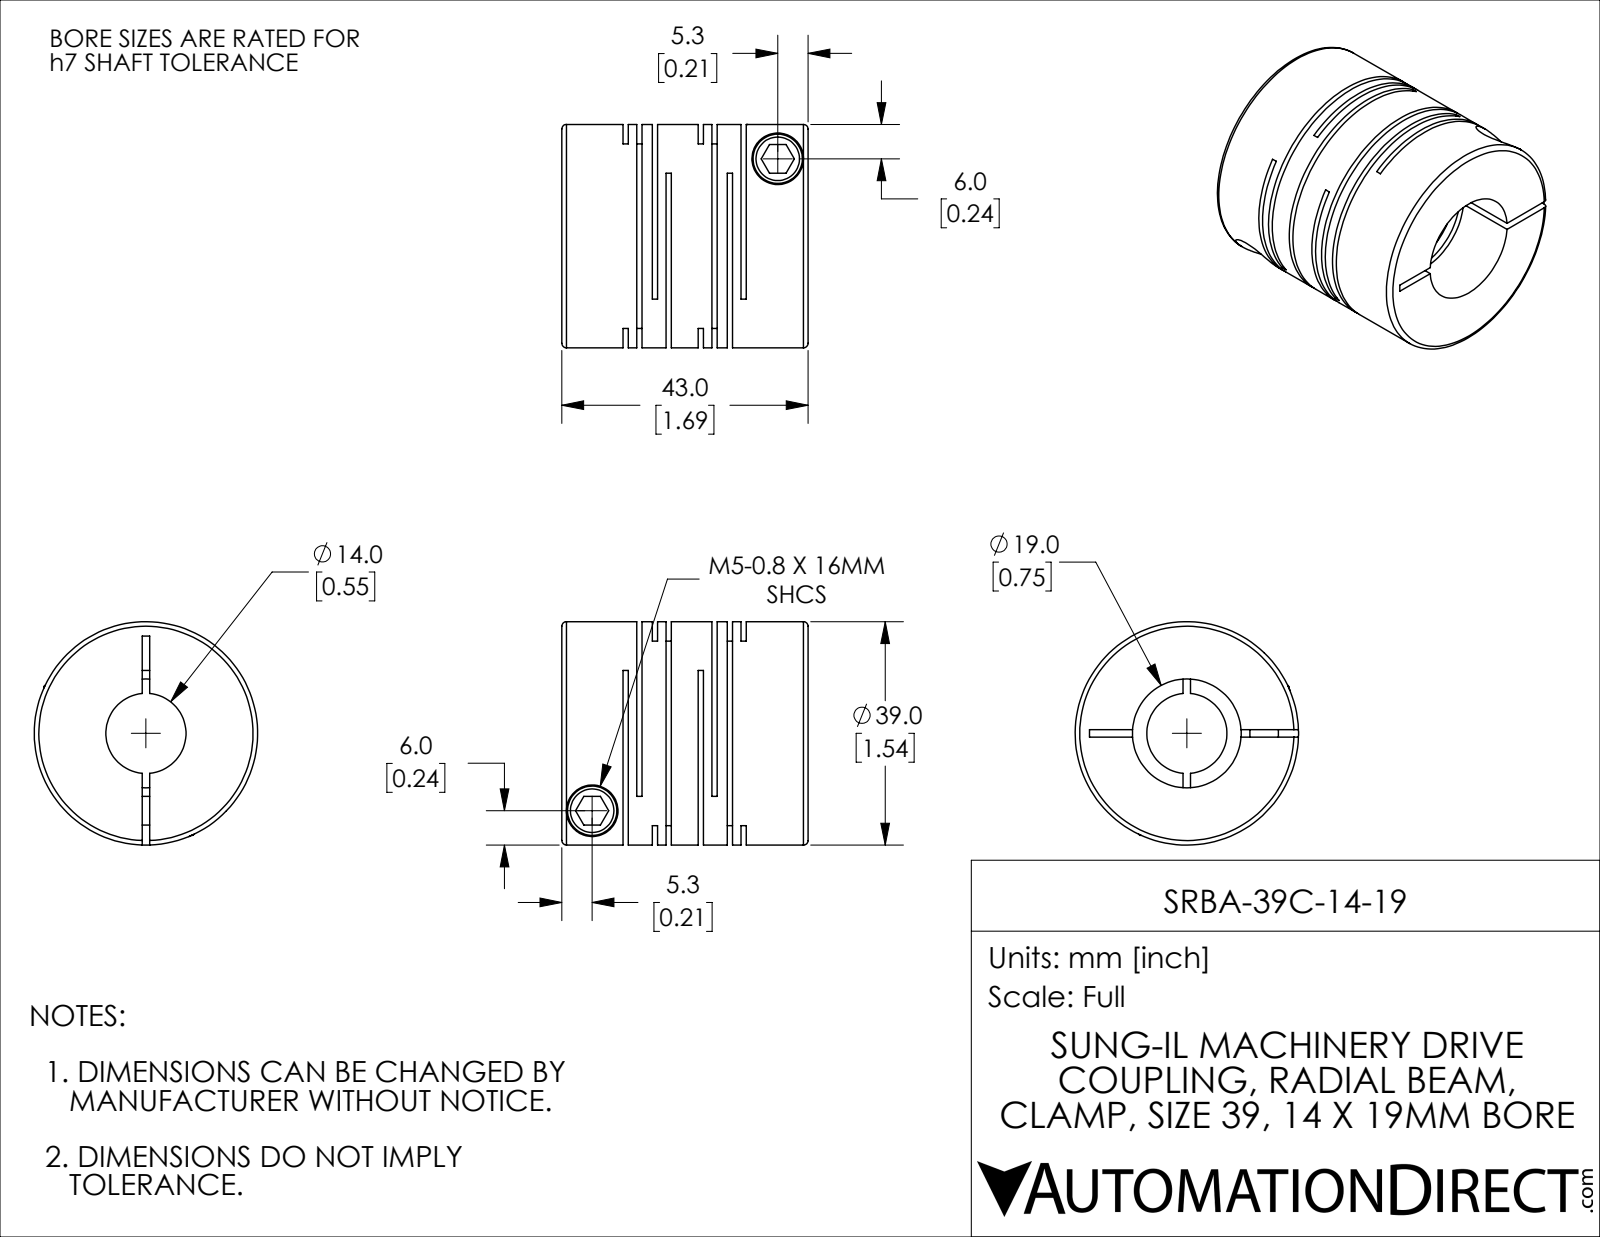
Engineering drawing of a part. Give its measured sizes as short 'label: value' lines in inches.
name: SRBA-39C-14-19
written by: SolidWorks 2021 (CONFIG_CONTROL_DESIGN)
unit: in
bodies: 1 solid, 114 faces (60 planar, 42 cylindrical, 12 other)
size: 1.693 × 1.535 × 1.535
volume: 2.063 in³; area: 33.88 in²
holes: 2× ⌀0.197, 2× ⌀0.354, 1× ⌀0.551, 1× ⌀0.748
bosses: 2× ⌀0.339, 1× ⌀1.535
face distances: 0.516, 0.036, 0.094, 0.201, 0.421, 0.552, 0.717, 0.131, 0.61, 0.058
